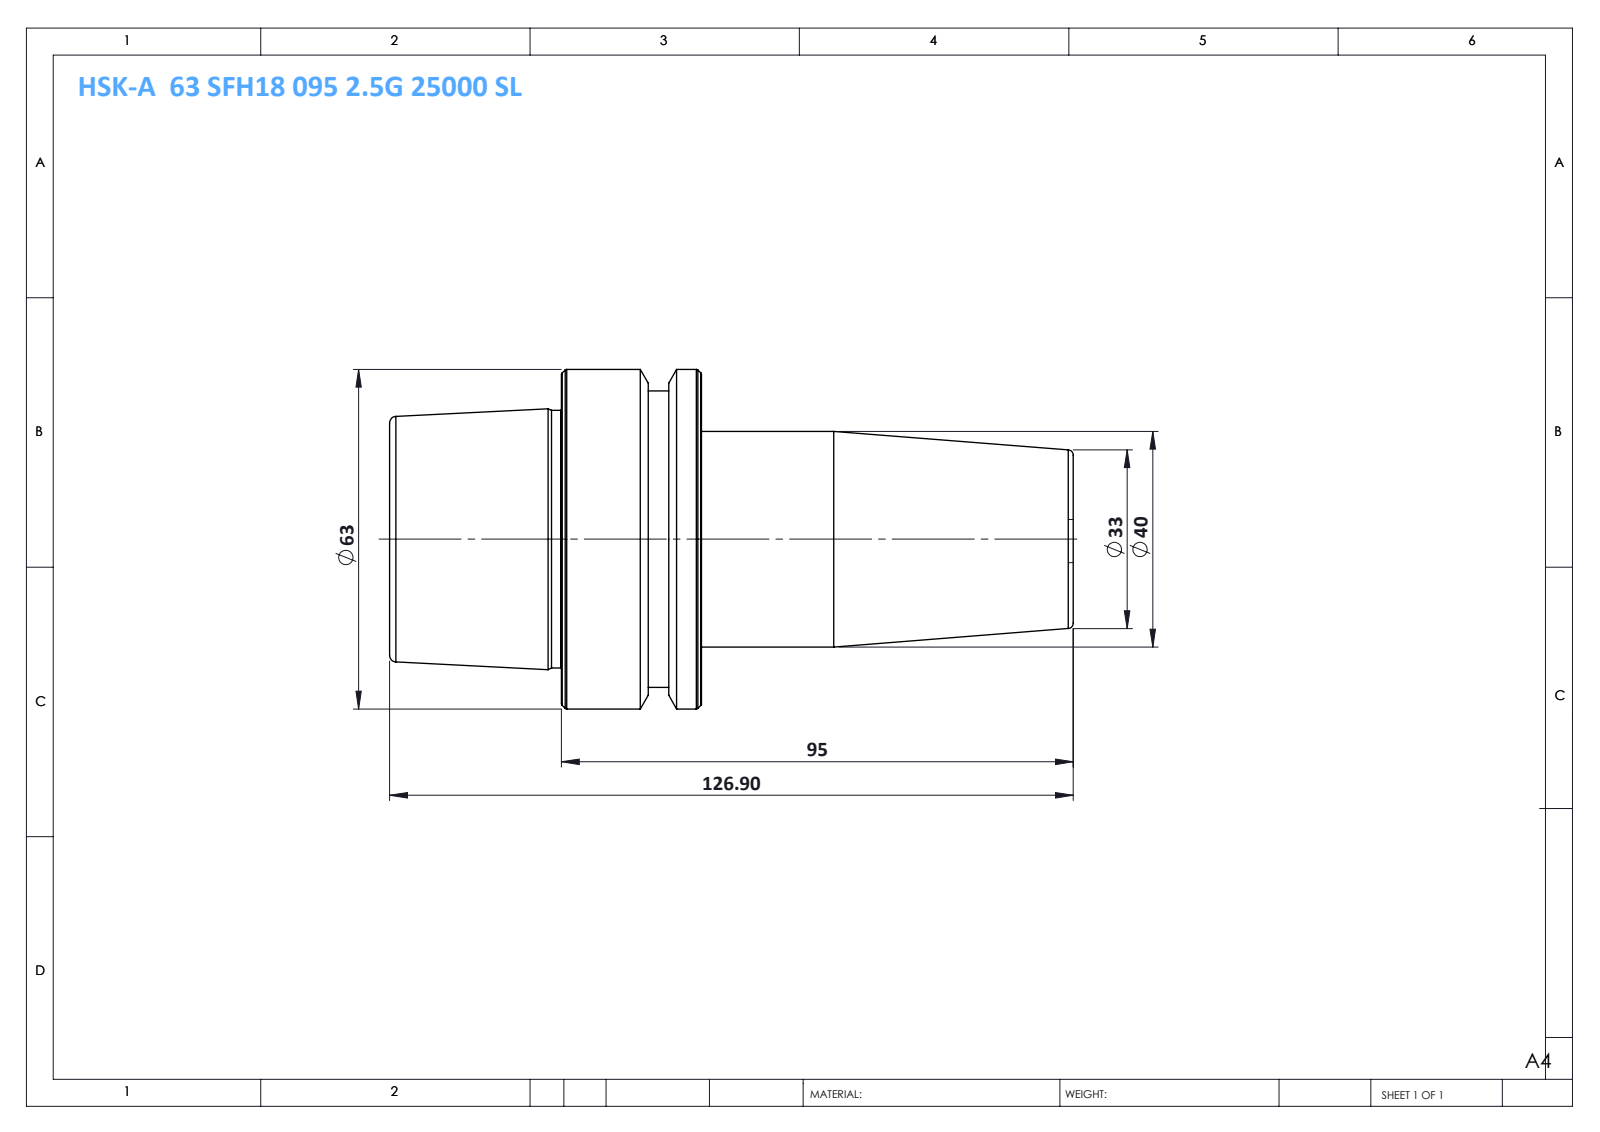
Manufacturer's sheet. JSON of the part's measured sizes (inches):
{"part_name": "HSK-A 63 SFH18 095 2.5G 25000 SL", "step_written_by": "SolidWorks 2014 (CONFIG_CONTROL_DESIGN)", "units": "inches", "bodies": {"solids": 1, "faces": 46, "planar": 6, "cylindrical": 10, "other": 30}, "overall_size": [4.996, 2.48, 2.48], "volume_in3": 12.82, "surface_area_in2": 37.83, "round_bosses_or_shafts": [[2.48, 1], [2.165, 1], [1.881, 1], [1.575, 1]], "face_to_face_distances": [2.28, 2.717, 4.996, 3.74, 1.024, 1.256, 2.957, 0.24, 0.783, 2.039]}
